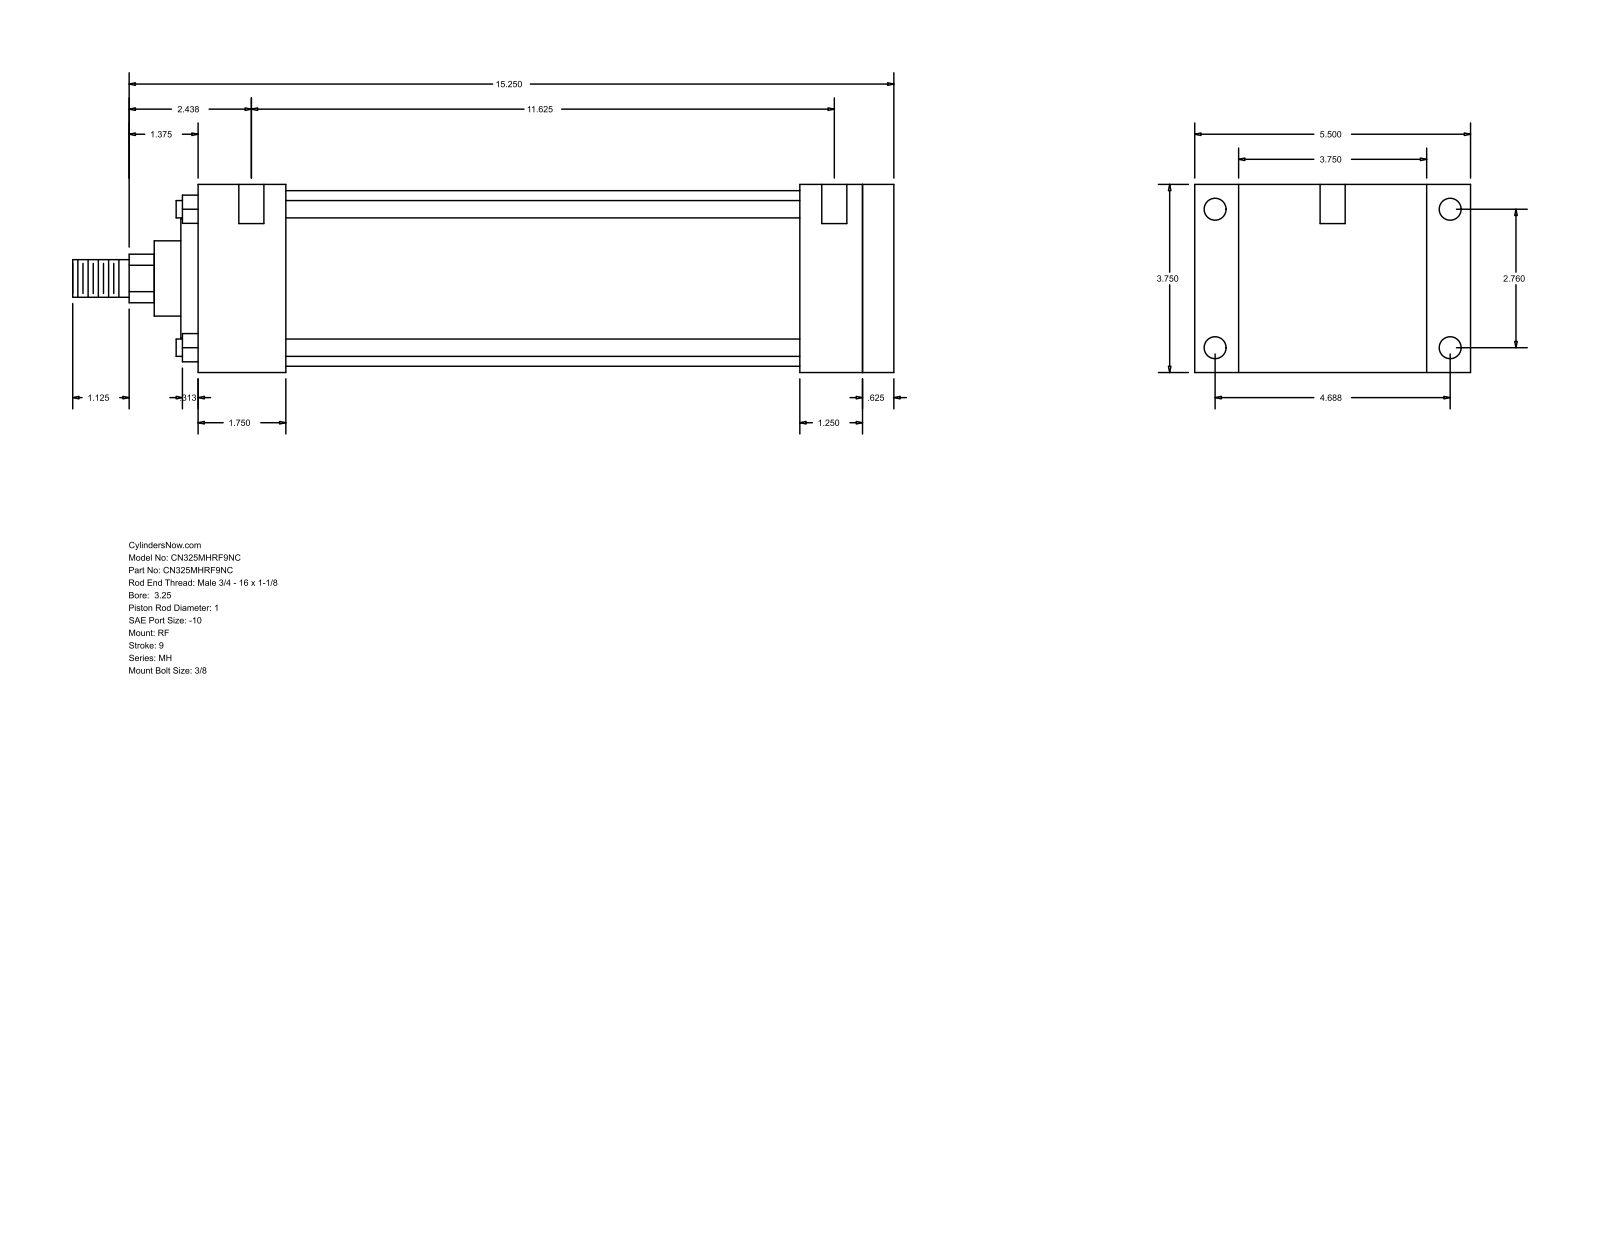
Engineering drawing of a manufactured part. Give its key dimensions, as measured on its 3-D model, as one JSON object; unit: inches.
{"part_name": "MH_RF__0325_1", "step_written_by": "GSSL Pune (CONFIG_CONTROL_DESIGN)", "units": "inches", "bodies": {"solids": 0, "faces": 94, "planar": 65, "cylindrical": 29, "other": 0}, "overall_size": [16.375, 5.5, 3.75], "round_holes": [[0.219, 4], [0.438, 4], [0.5, 2]], "round_bosses_or_shafts": [[0.345, 4], [3.5, 1], [2.375, 1], [1.5, 1], [1, 1], [0.75, 1]], "partial_cylinders_radius": [[0.484, 1]], "face_to_face_distances": [3.75, 13.875, 13.25, 0.625, 0.875, 4.625, 1.75, 11.5, 12.125, 12], "hole_center_spacings": [2.76, 4.687, 5.439, 11.875, 0.062, 0.187, 11.625, 11.687]}
